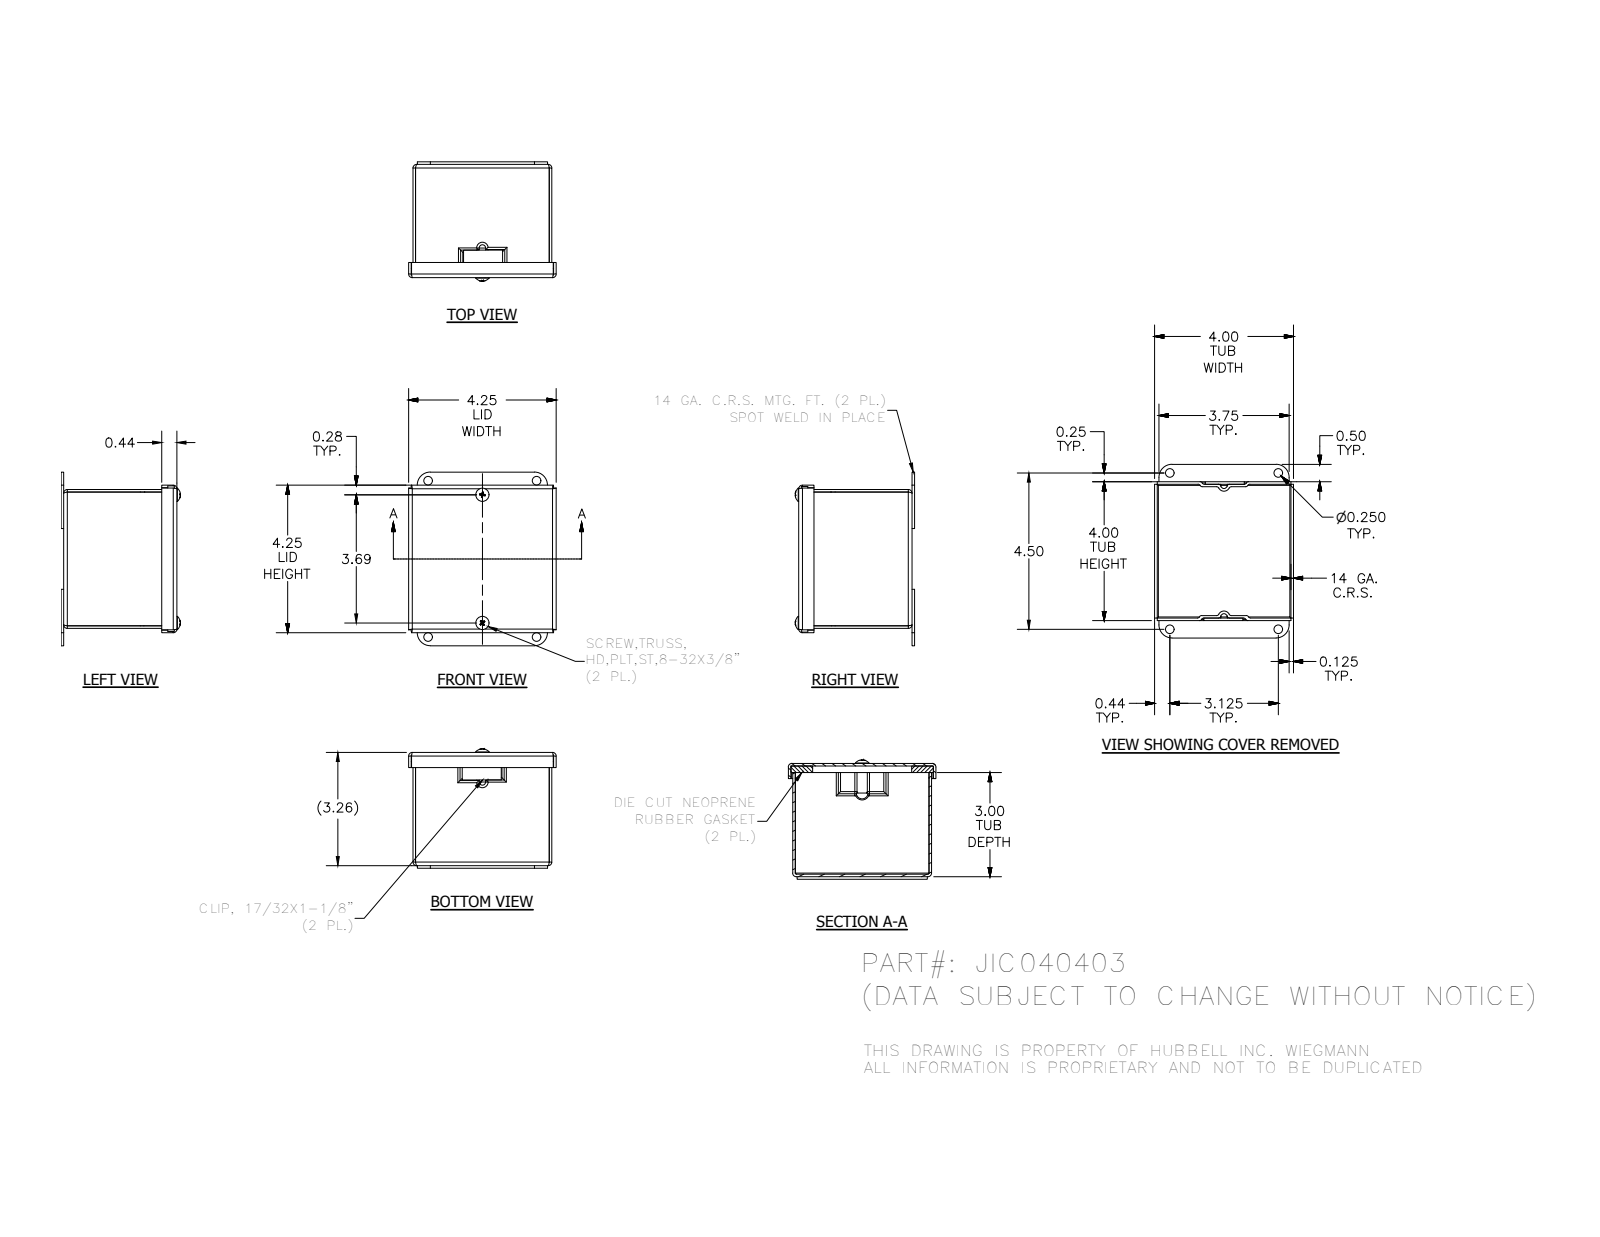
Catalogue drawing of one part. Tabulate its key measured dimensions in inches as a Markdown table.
| quantity | value |
| --- | --- |
| part name | JIC040403BKP; 31811; 372177; JIC0404MF (+3 more) |
| STEP written by | Autodesk Inventor 2014 (AUTOMOTIVE_DESIGN) |
| units | inches |
| bodies | 10 solids, 278 faces (136 planar, 78 cylindrical, 64 other) |
| overall size | 5.023 × 4.283 × 3.451 |
| volume | 8.919 in³ |
| surface area | 226.4 in² |
| round holes (diameter × count) | 0.25 × 4, 0.219 × 2 |
| round bosses / shafts (diameter × count) | 0.384 × 2, 0.164 × 2 |
| partial cylindrical surfaces (radius × count) | 0.071 × 38, 0.031 × 8, 0.105 × 8, 0.094 × 4, 0.375 × 4, 0.168 × 2 |
| main face-to-face distances | 0.074, 3.926, 3.852, 4, 3.188, 3.261, 3.187, 0.074, 3.114, 3.262 |
| hole center spacings | 3.125, 4.383, 4.383, 1.613, 1.614, 1.614, 1.615, 3.69 |
